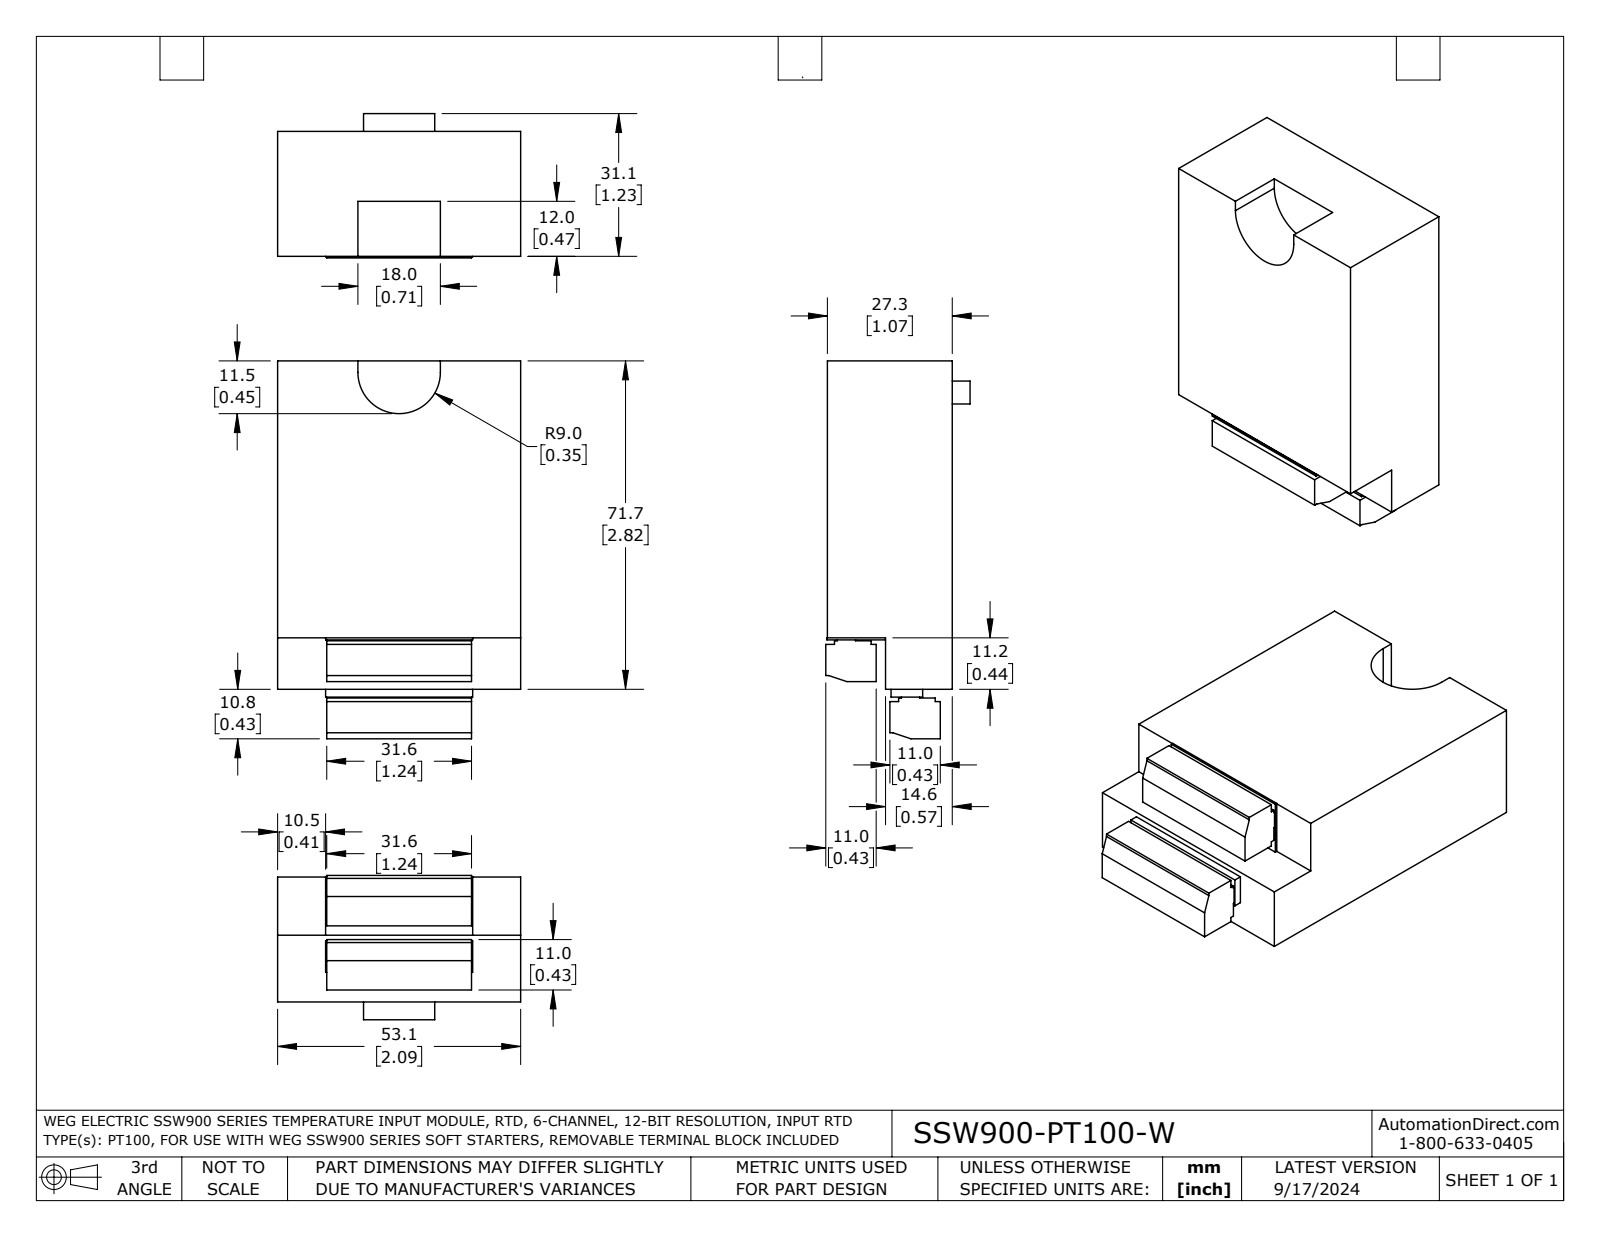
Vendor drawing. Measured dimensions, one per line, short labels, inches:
name: SSW900-PT100-W
written by: SolidWorks 2021 (AUTOMOTIVE_DESIGN)
unit: in
bodies: 1 solid, 58 faces (57 planar, 1 cylindrical, 0 other)
size: 3.246 × 2.089 × 1.24
volume: 6.146 in³; area: 26.27 in²
rounds: 1× R0.354
face distances: 1.073, 2.089, 0.573, 0.5, 2.821, 0.551, 0.491, 0.433, 0.358, 0.424
